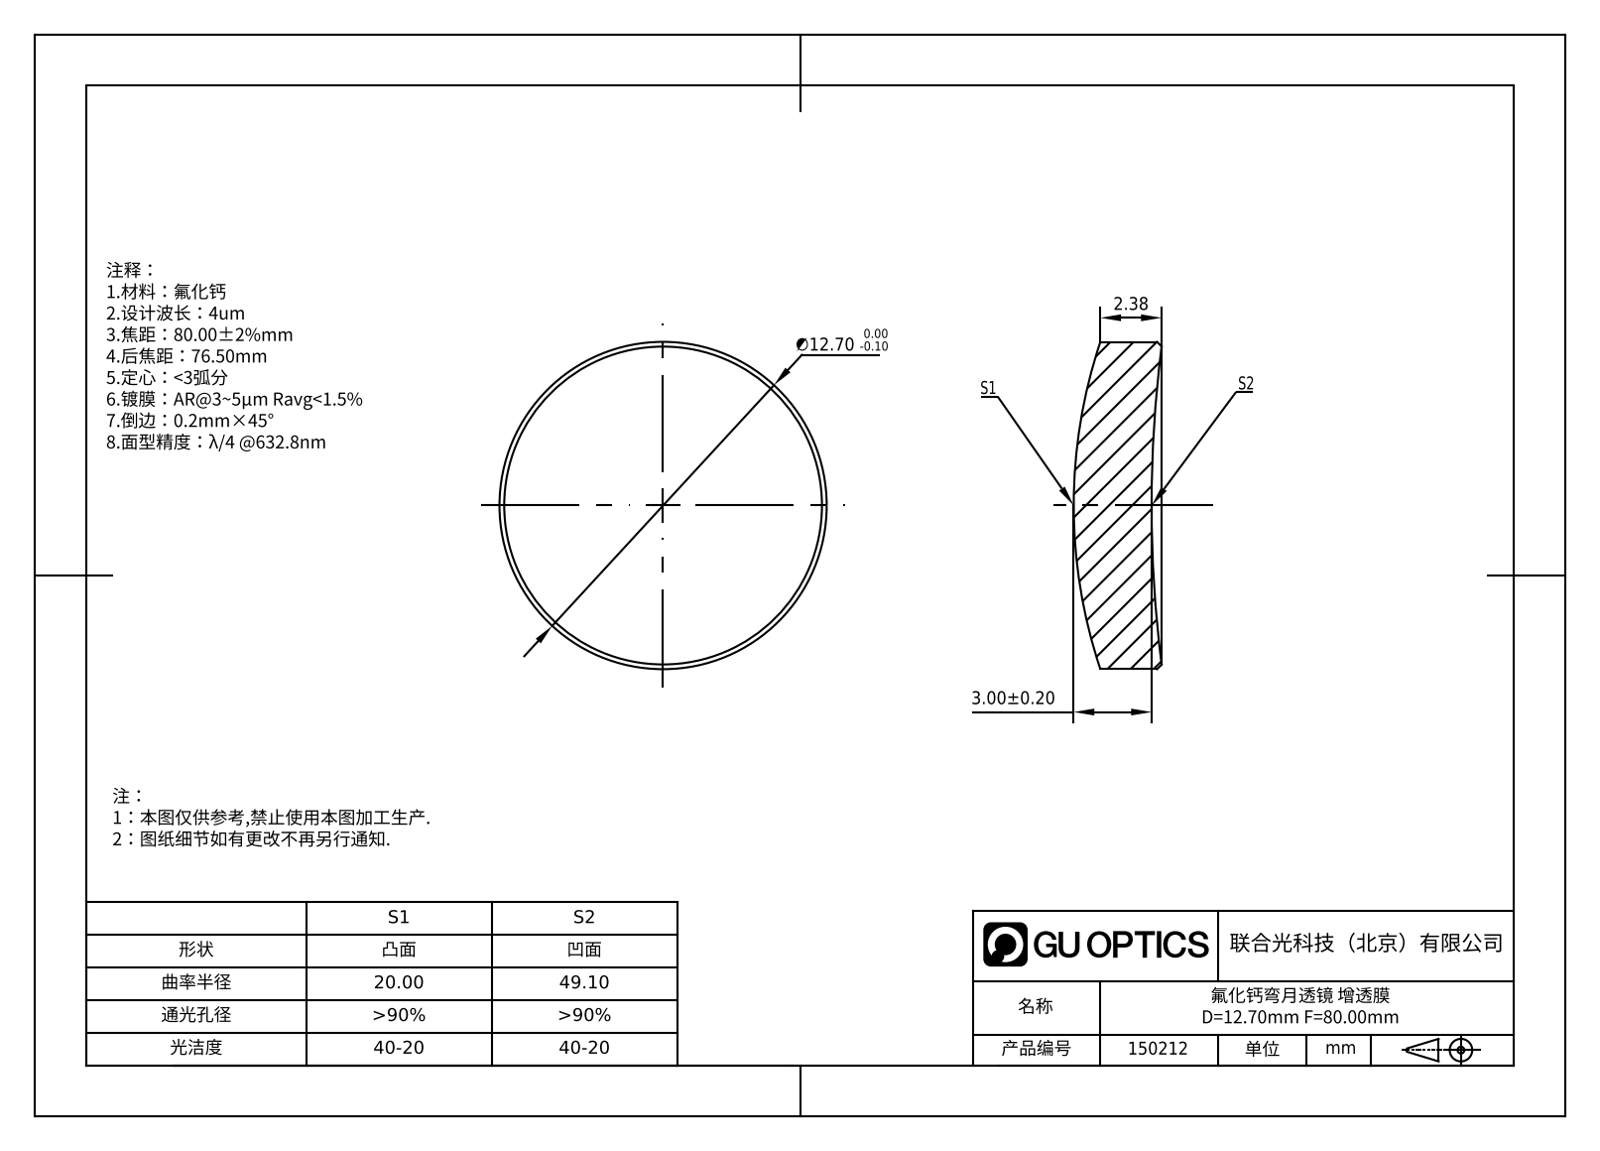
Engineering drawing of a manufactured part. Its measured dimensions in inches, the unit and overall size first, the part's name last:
Units: inches
Overall size (bounding box): 0.5 × 0.5 × 0.134
Round bosses / shafts (diameter × count): ⌀0.5 ×1
Volume: 0.021 in³ · Surface area: 0.539 in²
Bodies: 1 solid, 8 faces (0 planar, 2 cylindrical, 6 other)
Part name (STEP PRODUCT): GLM5-012B-080-IR1
STEP written by: SolidWorks 2022 (AUTOMOTIVE_DESIGN)
